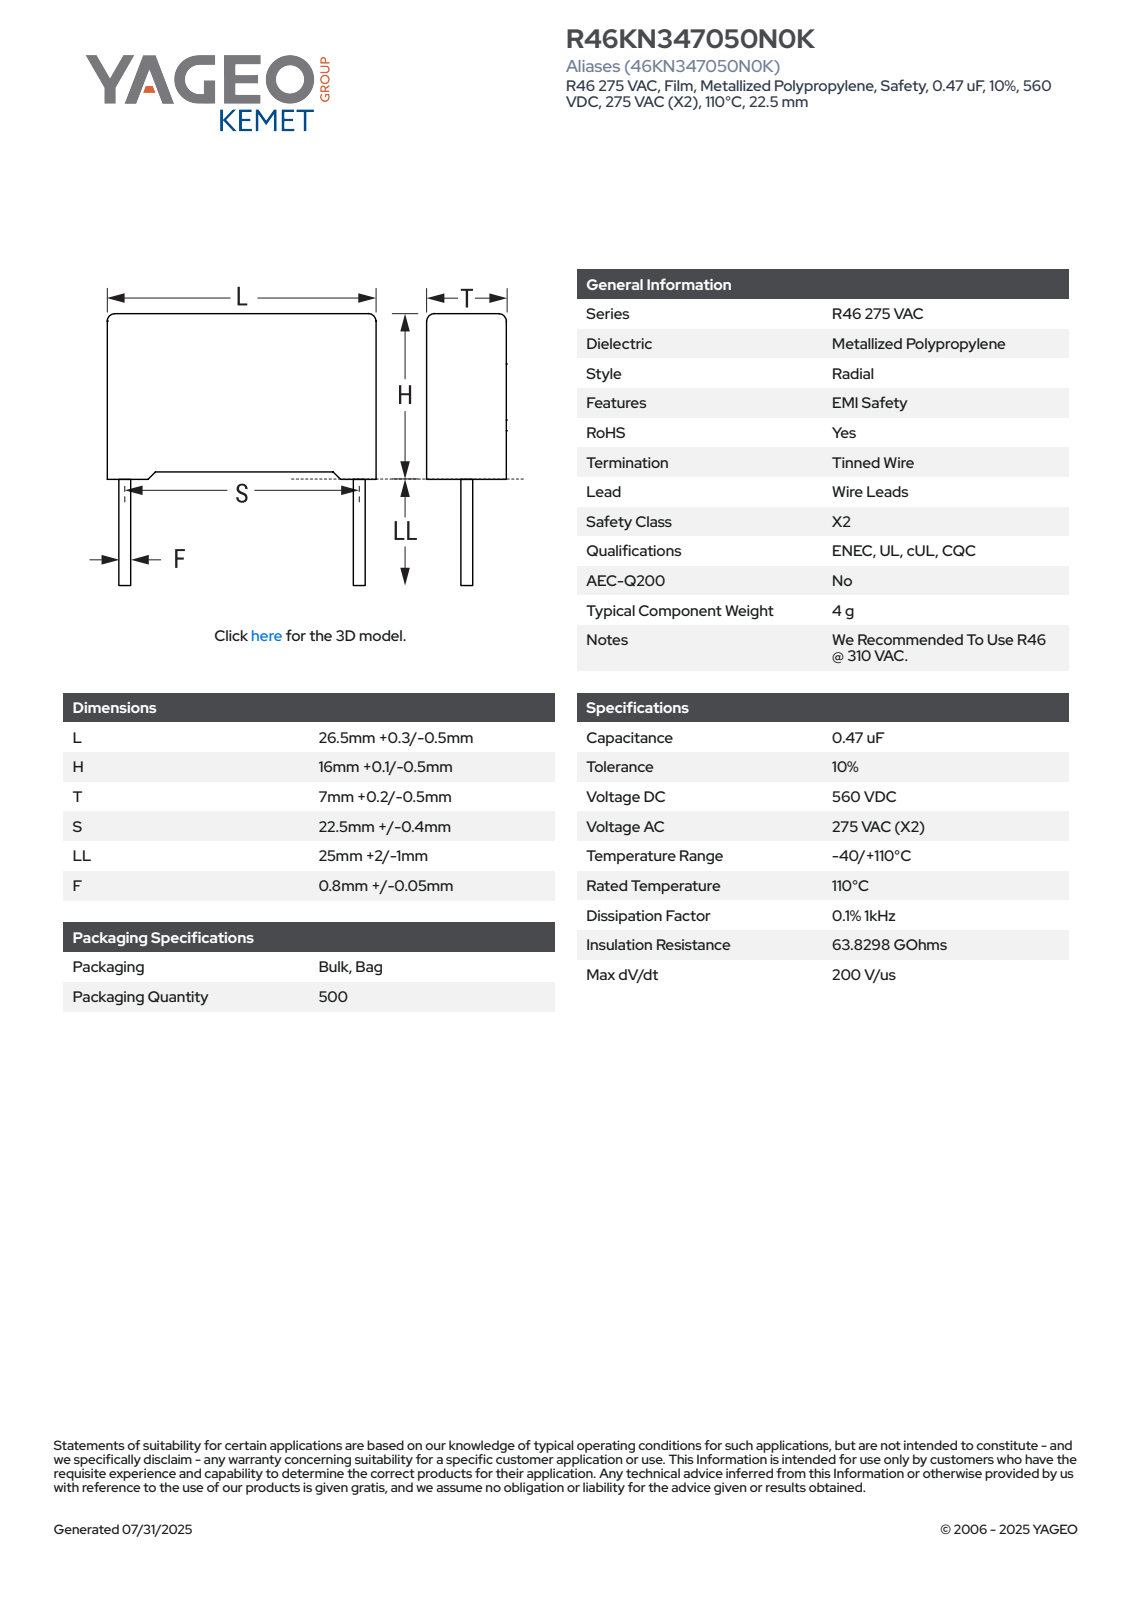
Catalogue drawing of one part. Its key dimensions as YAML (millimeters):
part_name: "CFR_RB2_26.5X16X7_L26.8H16.1T7.2S22.5LL27F0.85"
step_written_by: "SolidWorks 2021 (AUTOMOTIVE_DESIGN)"
units: millimeters
bodies: {solids: 4, faces: 85, planar: 77, cylindrical: 8, other: 0}
overall_size: [43.1, 26.8, 7.21]
volume: 3015
surface_area: 1673
round_bosses_or_shafts:
  - {diameter: 0.85, count: 2}
partial_cylinders:
  - {radius: 0.5, count: 4}
face_to_face_distances: [7.2, 15.35, 26.8, 15.54, 0.89, 0.56, 0.75, 16.1, 6.31, 5.42]
